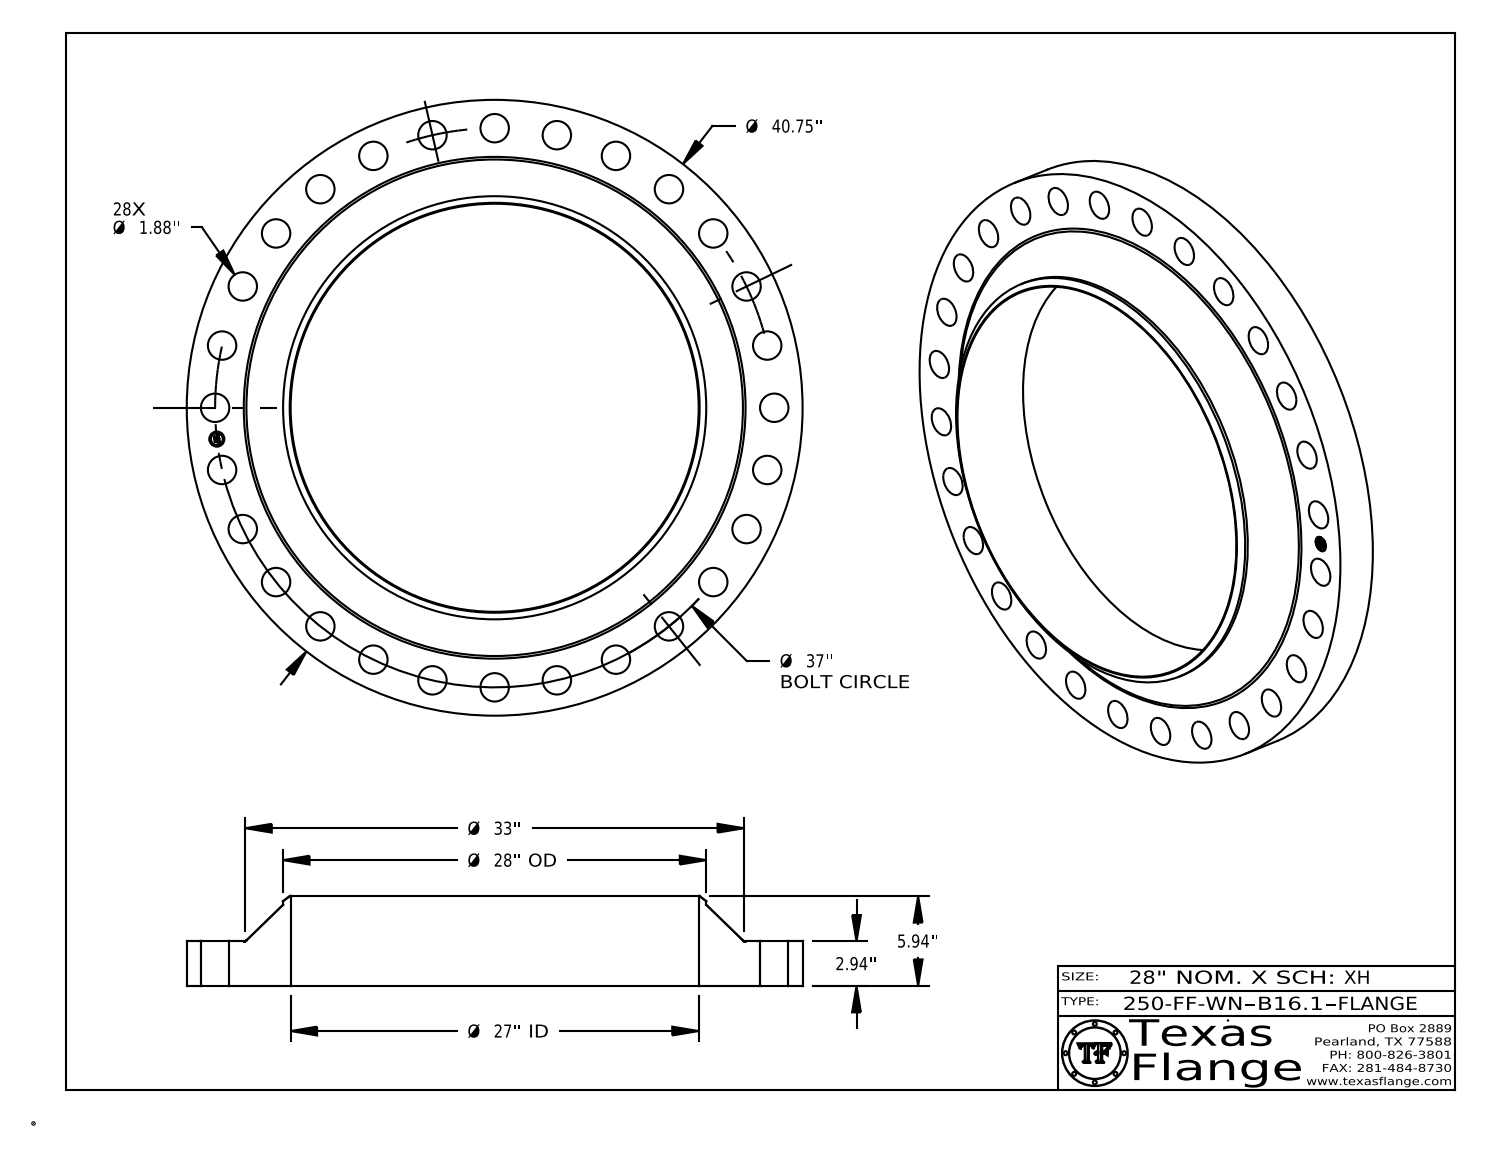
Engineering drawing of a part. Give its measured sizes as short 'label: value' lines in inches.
name: 250-FF-WN, B16.1
written by: CATIA V5 STEP AP214 (AUTOMOTIVE_DESIGN)
unit: in
bodies: 1 solid, 456 faces (368 planar, 82 cylindrical, 6 other)
size: 40.75 × 40.75 × 5.94
volume: 2 329 in³; area: 2 798 in²
holes: 28× ⌀1.88, 1× ⌀1, 1× ⌀27
bosses: 8× ⌀0.061, 1× ⌀40.75, 1× ⌀28, 1× ⌀0.788
face distances: 2.94, 5.94, 3, 0.015, 2.925, 3.015, 0.298, 0.292, 0.054, 0.193
hole spacings: 18.5, 26.163, 31.329, 36.072, 36.767, 33.336, 4.143, 16.054
